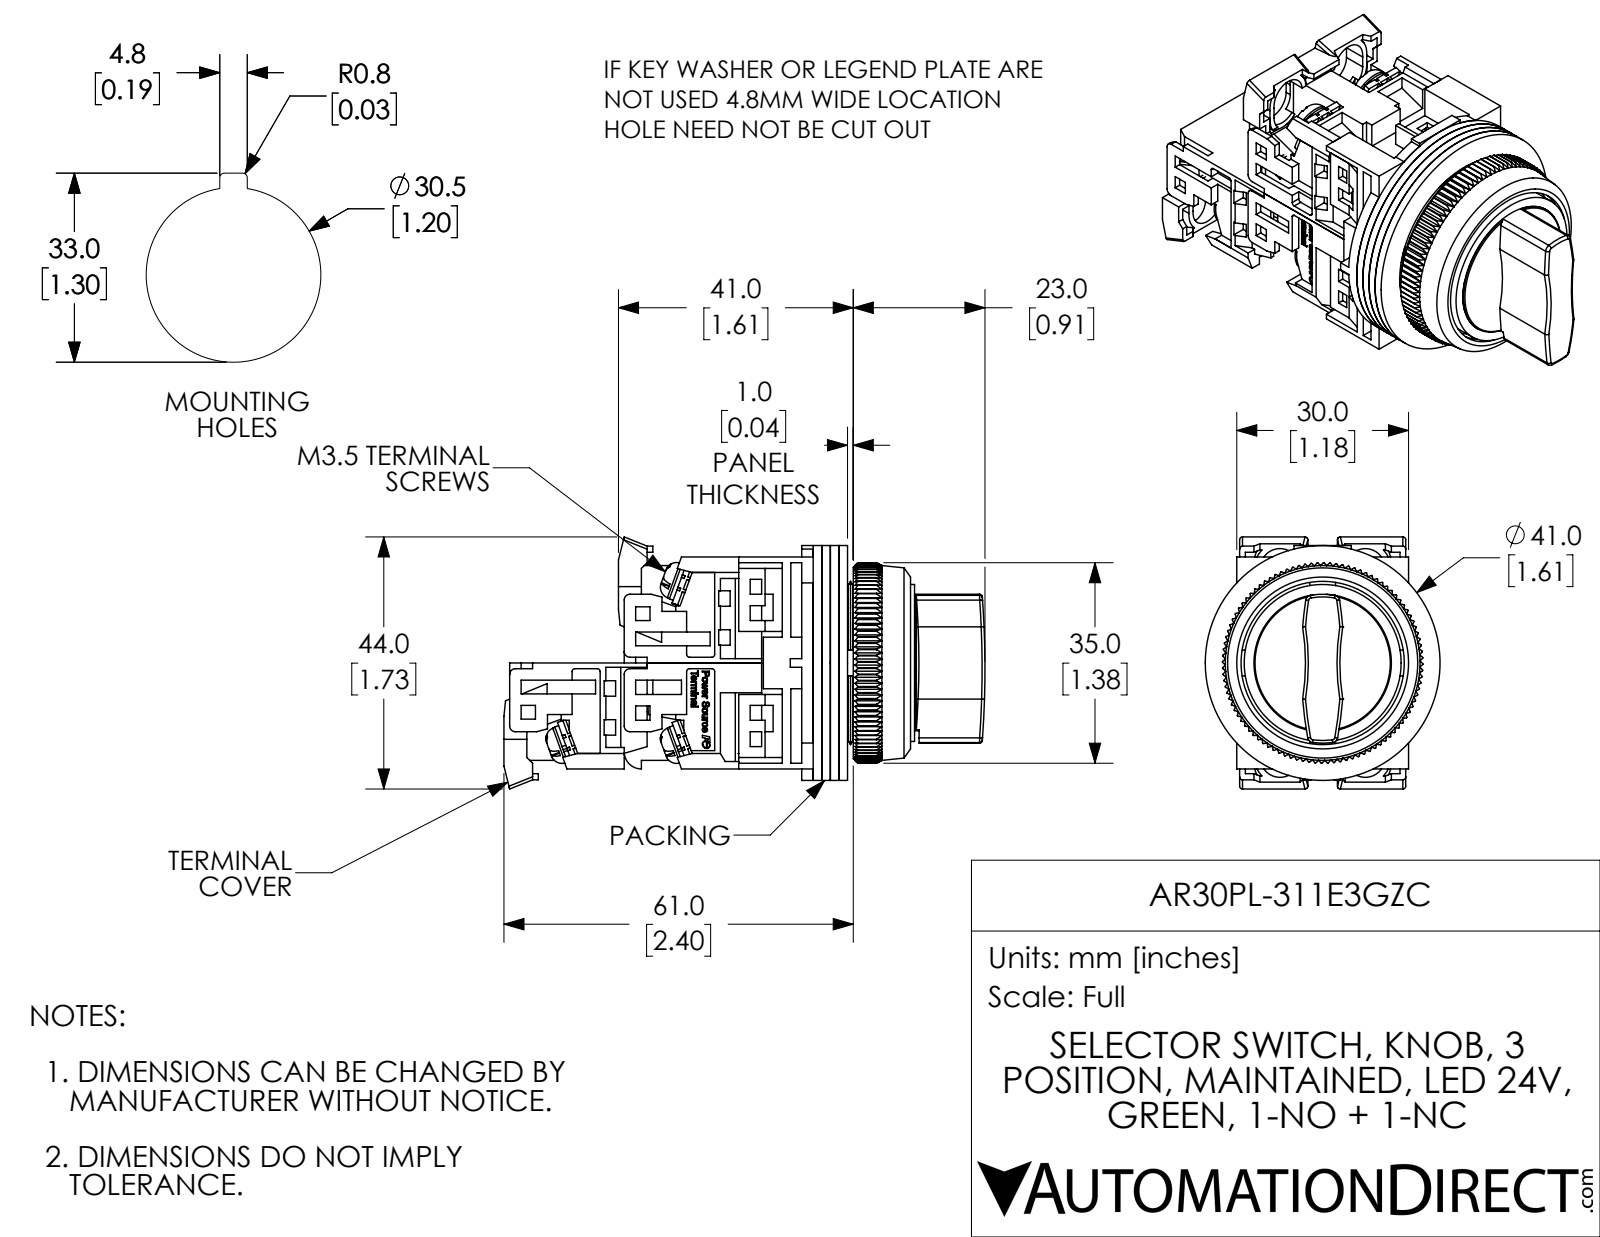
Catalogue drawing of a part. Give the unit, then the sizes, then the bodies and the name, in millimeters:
Units: millimetres
Overall size (bounding box): 84 × 44 × 41
Round holes (diameter × count): ⌀3.5 ×10, ⌀3.6 ×6, ⌀3 ×1, ⌀12 ×1, ⌀18 ×1, ⌀19.5 ×1, ⌀21 ×1, ⌀28.5 ×1, ⌀30 ×1, ⌀31.8 ×1
Round bosses / shafts (diameter × count): ⌀6.6 ×6, ⌀3.5 ×6, ⌀1.6 ×2, ⌀41 ×1, ⌀29.2 ×1, ⌀27.4 ×1, ⌀24 ×1, ⌀22.5 ×1
Partial cylindrical surfaces — rounded edges, fillets, slot ends (radius × count): R1.5 ×24, R0.5 ×14, R1 ×10, R3.5 ×4, R4.5 ×4, R3 ×3, R40 ×2, R75 ×2
Main face-to-face distances: 1.5, 3, 4.5, 1, 20, 1.6, 2, 0.5, 20.6, 17.5
Hole centre spacings: 14.7, 6.8, 16.2, 15.5
Volume: 43 870 mm³ · Surface area: 42 930 mm²
Bodies: 32 solids, 2783 faces (2039 planar, 338 cylindrical, 406 other)
Part name (STEP PRODUCT): AR30PL-311E3GZC
STEP written by: SolidWorks 2017 (AUTOMOTIVE_DESIGN)
